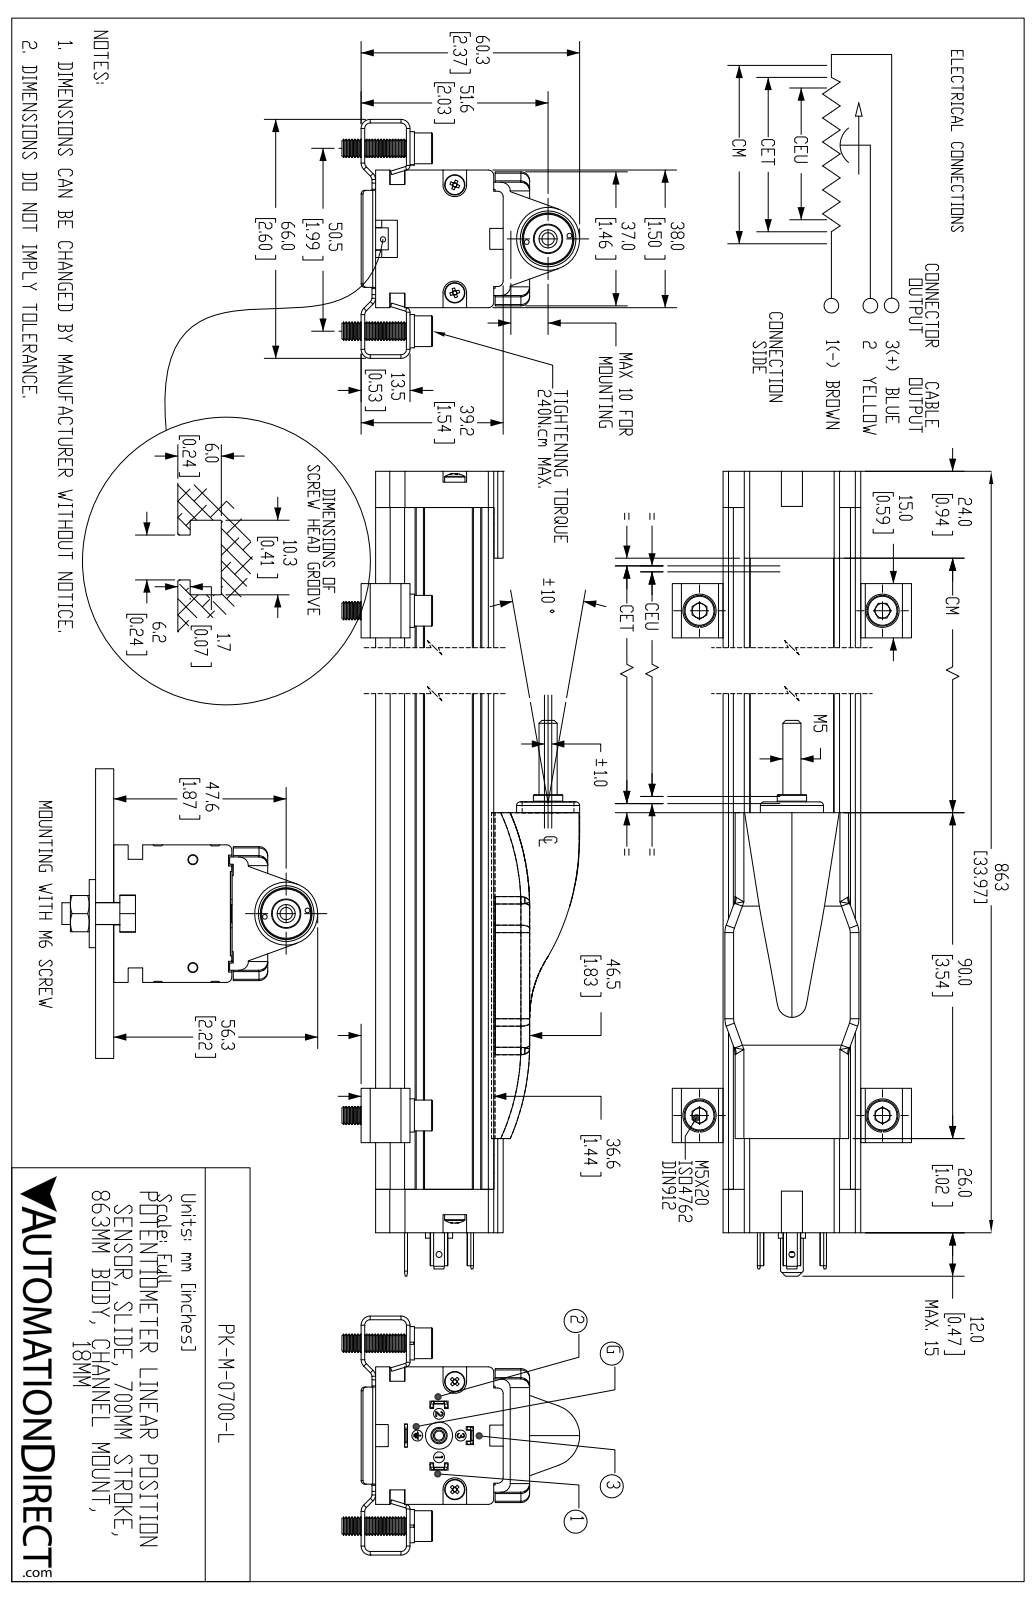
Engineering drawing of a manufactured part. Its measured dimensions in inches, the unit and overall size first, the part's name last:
Units: inches
Overall size (bounding box): 34.449 × 2.598 × 2.583
Round holes (diameter × count): ⌀0.118 ×5, ⌀0.201 ×4, ⌀0.051 ×2, ⌀0.059 ×2, ⌀0.065 ×2, ⌀0.102 ×2, ⌀0.108 ×2, ⌀0.13 ×2, ⌀0.209 ×2, ⌀0.063 ×1, ⌀0.098 ×1, ⌀0.157 ×1
Round bosses / shafts (diameter × count): ⌀0.197 ×7, ⌀0.362 ×4, ⌀0.335 ×4, ⌀0.22 ×2, ⌀0.118 ×2, ⌀0.098 ×2, ⌀0.685 ×1, ⌀0.551 ×1
Partial cylindrical surfaces — rounded edges, fillets, slot ends (radius × count): R0.039 ×28, R0.059 ×12, R0.098 ×8, R0.104 ×8, R0.236 ×8, R0.033 ×6, R0.094 ×6, R0.024 ×4
Main face-to-face distances: 1.268, 0.157, 1.272, 1.496, 0.079, 1.035, 0.236, 0.315, 1.031, 0.02
Hole centre spacings: 0.236, 0.334, 0.234, 0.39, 0.472, 0.484, 0.539, 0.59
Volume: 61.86 in³ · Surface area: 377.7 in²
Bodies: 27 solids, 1761 faces (785 planar, 384 cylindrical, 592 other)
Part name (STEP PRODUCT): PK-M-0700-L
STEP written by: SolidWorks 2019 (AUTOMOTIVE_DESIGN)
